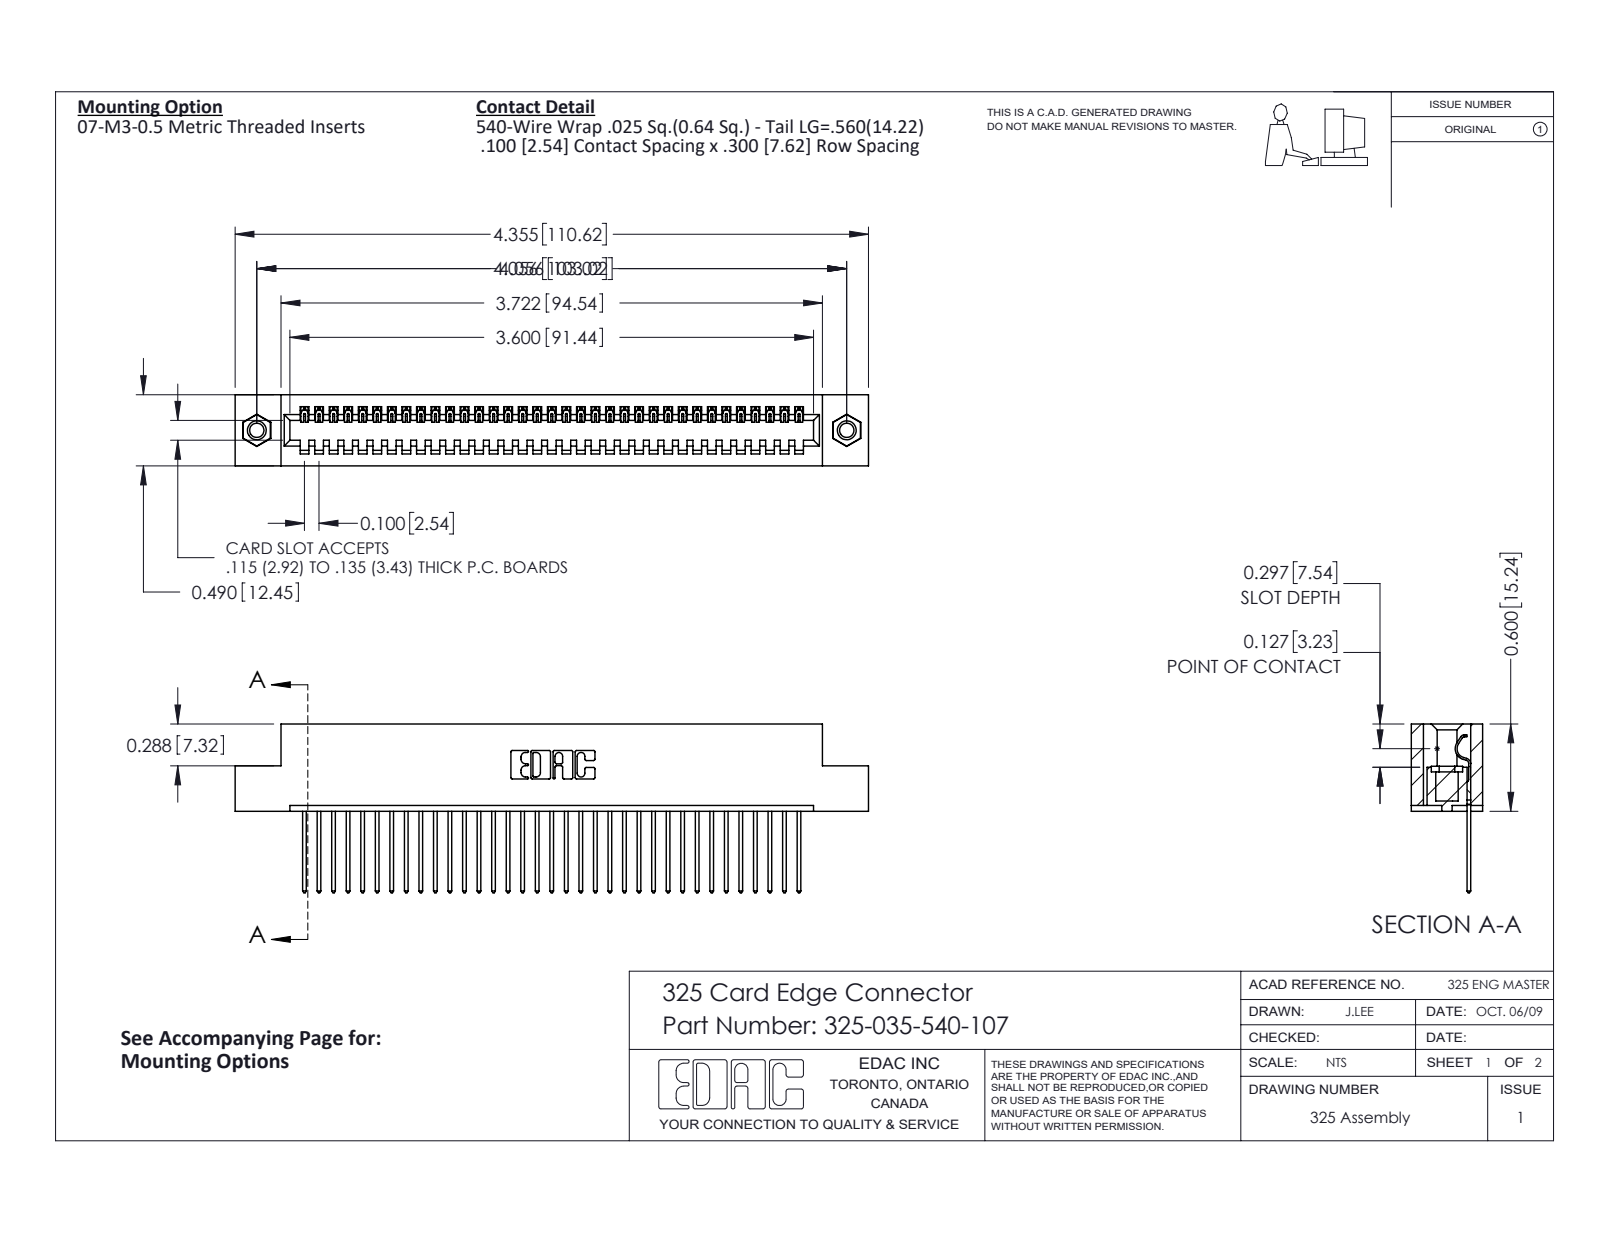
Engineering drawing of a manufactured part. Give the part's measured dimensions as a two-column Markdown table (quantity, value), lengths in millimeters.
| quantity | value |
| --- | --- |
| part name | 325 Part_TI; 325-035-540-107; 345-250-001_345-250-005-103; 325-292-001_325-293-140 |
| STEP written by | SolidWorks 2016 (CONFIG_CONTROL_DESIGN) |
| units | millimeters |
| bodies | 38 solids, 2204 faces (1572 planar, 616 cylindrical, 16 other) |
| overall size | 110.6 × 29.5 × 12.4 |
| volume | 14 000 mm³ |
| surface area | 15 580 mm² |
| round holes (diameter × count) | 2.5 × 2, 3.2 × 2, 4.1 × 2 |
| round bosses / shafts (diameter × count) | 3.9 × 2 |
| partial cylindrical surfaces (radius × count) | 0.2 × 70, 0.3 × 70, 0.3 × 22, 0.2 × 6, 0.8 × 6, 0.7 × 3, 0.4 × 1, 0.6 × 1 |
| main face-to-face distances | 2.1, 10.3, 12.4, 7.6, 2.7, 9.7, 0.6, 8.3, 14.2, 15.2 |
| hole center spacings | 103 |
